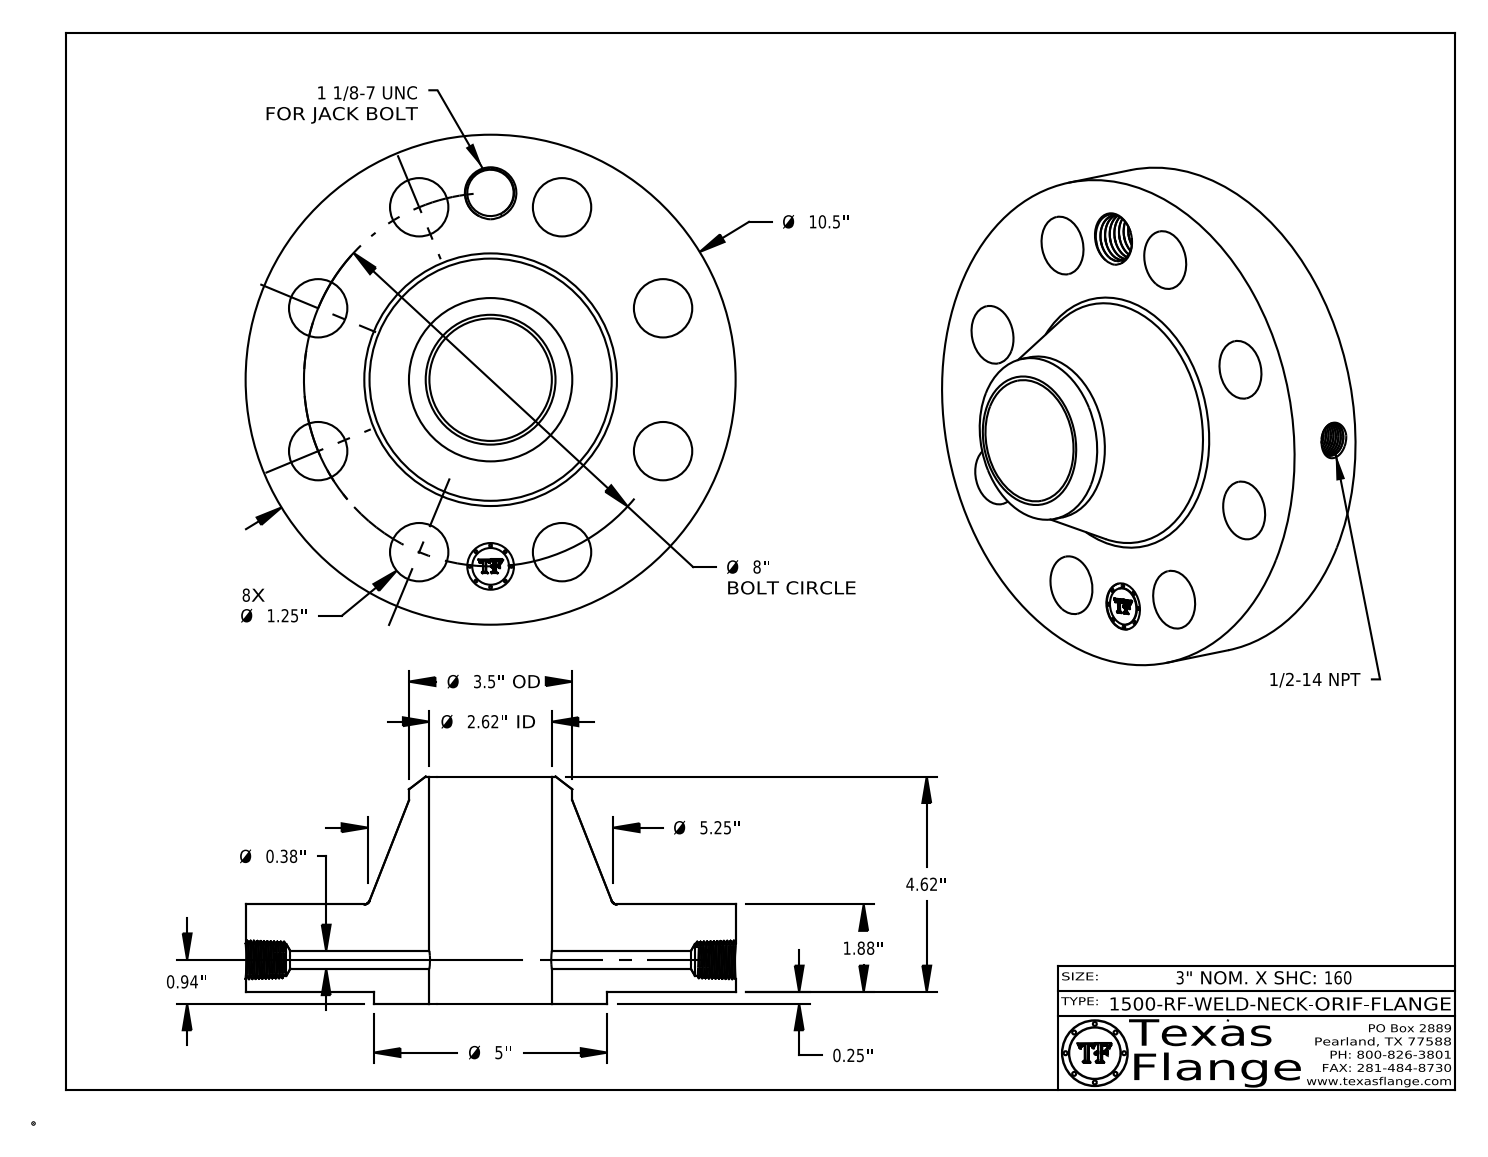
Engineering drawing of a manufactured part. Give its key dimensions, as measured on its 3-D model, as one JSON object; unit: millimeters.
{"part_name": "1500-RF-WELD-NECK", "step_written_by": "CATIA V5 STEP AP214 (AUTOMOTIVE_DESIGN)", "units": "millimeters", "bodies": {"solids": 1, "faces": 760, "planar": 369, "cylindrical": 90, "other": 301}, "overall_size": [266.7, 266.7, 123.7], "volume_mm3": 2592000, "surface_area_mm2": 227500, "round_holes": [[31.8, 8], [9.5, 1], [17.1, 1], [25, 1], [25.4, 1], [66.6, 1]], "round_bosses_or_shafts": [[1.5, 8], [266.7, 1], [127, 1], [88.9, 1], [20, 1]], "face_to_face_distances": [47.8, 6.4, 54.1, 123.7, 117.3, 69.6, 53.7, 47.4, 0.4, 70], "hole_center_spacings": [101.6, 143.7, 187.7, 39.6, 77.7, 77.8, 112.9, 169]}
